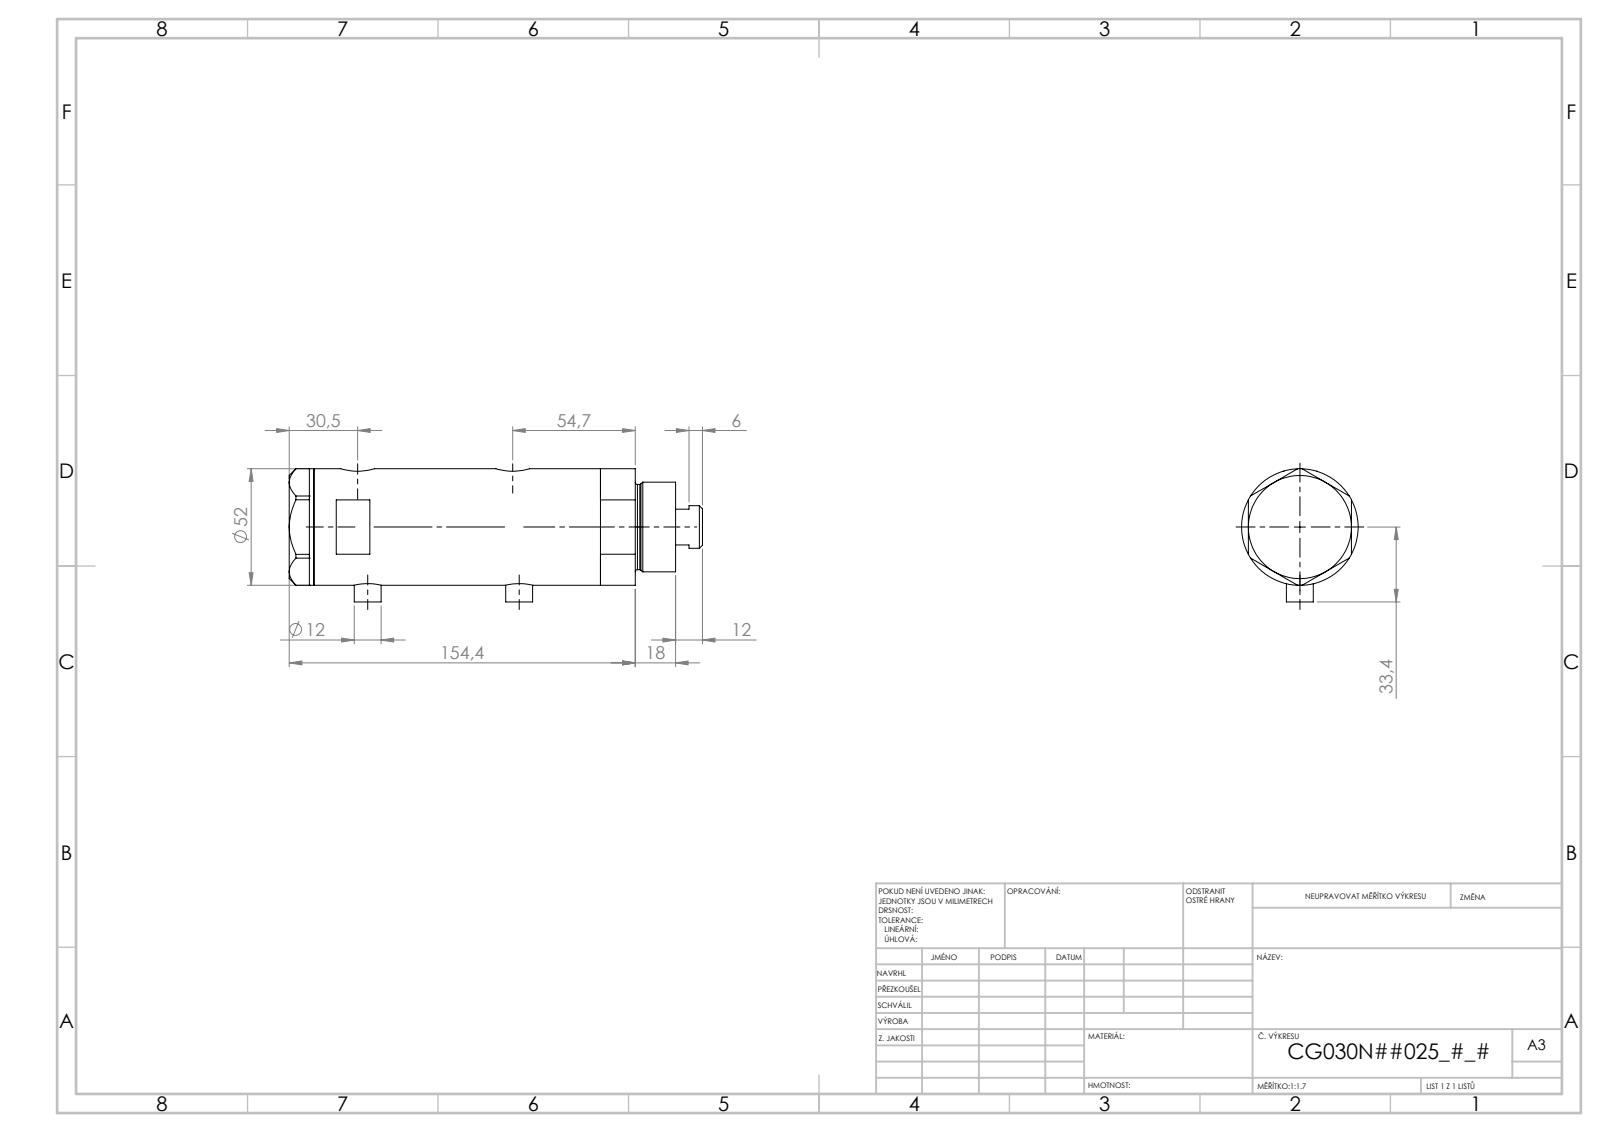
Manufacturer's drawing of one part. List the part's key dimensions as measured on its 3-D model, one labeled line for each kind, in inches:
Part name (STEP PRODUCT): V270CG_BACK; V270CG_MIDDLE; V270CG_VC; V270CG_FRONT
STEP written by: SolidWorks 2019 (CONFIG_CONTROL_DESIGN)
Units: inches
Bodies: 4 solids, 140 faces (67 planar, 53 cylindrical, 20 other)
Overall size (bounding box): 6.851 × 2.091 × 2.047
Volume: 18.97 in³ · Surface area: 113.3 in²
Round holes (diameter × count): ⌀0.197 ×2, ⌀0.383 ×2, ⌀0.492 ×2, ⌀0.591 ×2, ⌀0.256 ×1, ⌀0.787 ×1, ⌀0.846 ×1, ⌀1.181 ×1, ⌀1.299 ×1, ⌀1.732 ×1
Round bosses / shafts (diameter × count): ⌀0.472 ×2, ⌀2.047 ×1, ⌀1.575 ×1, ⌀1.496 ×1, ⌀0.748 ×1
Main face-to-face distances: 0.937, 0.433, 1.37, 1.811, 3.526, 3.093, 2.156, 4.959, 4.526, 3.589
Hole centre spacings: 0.114, 0.177, 2.037, 2.152, 2.215, 2.329, 0.114, 0.115
